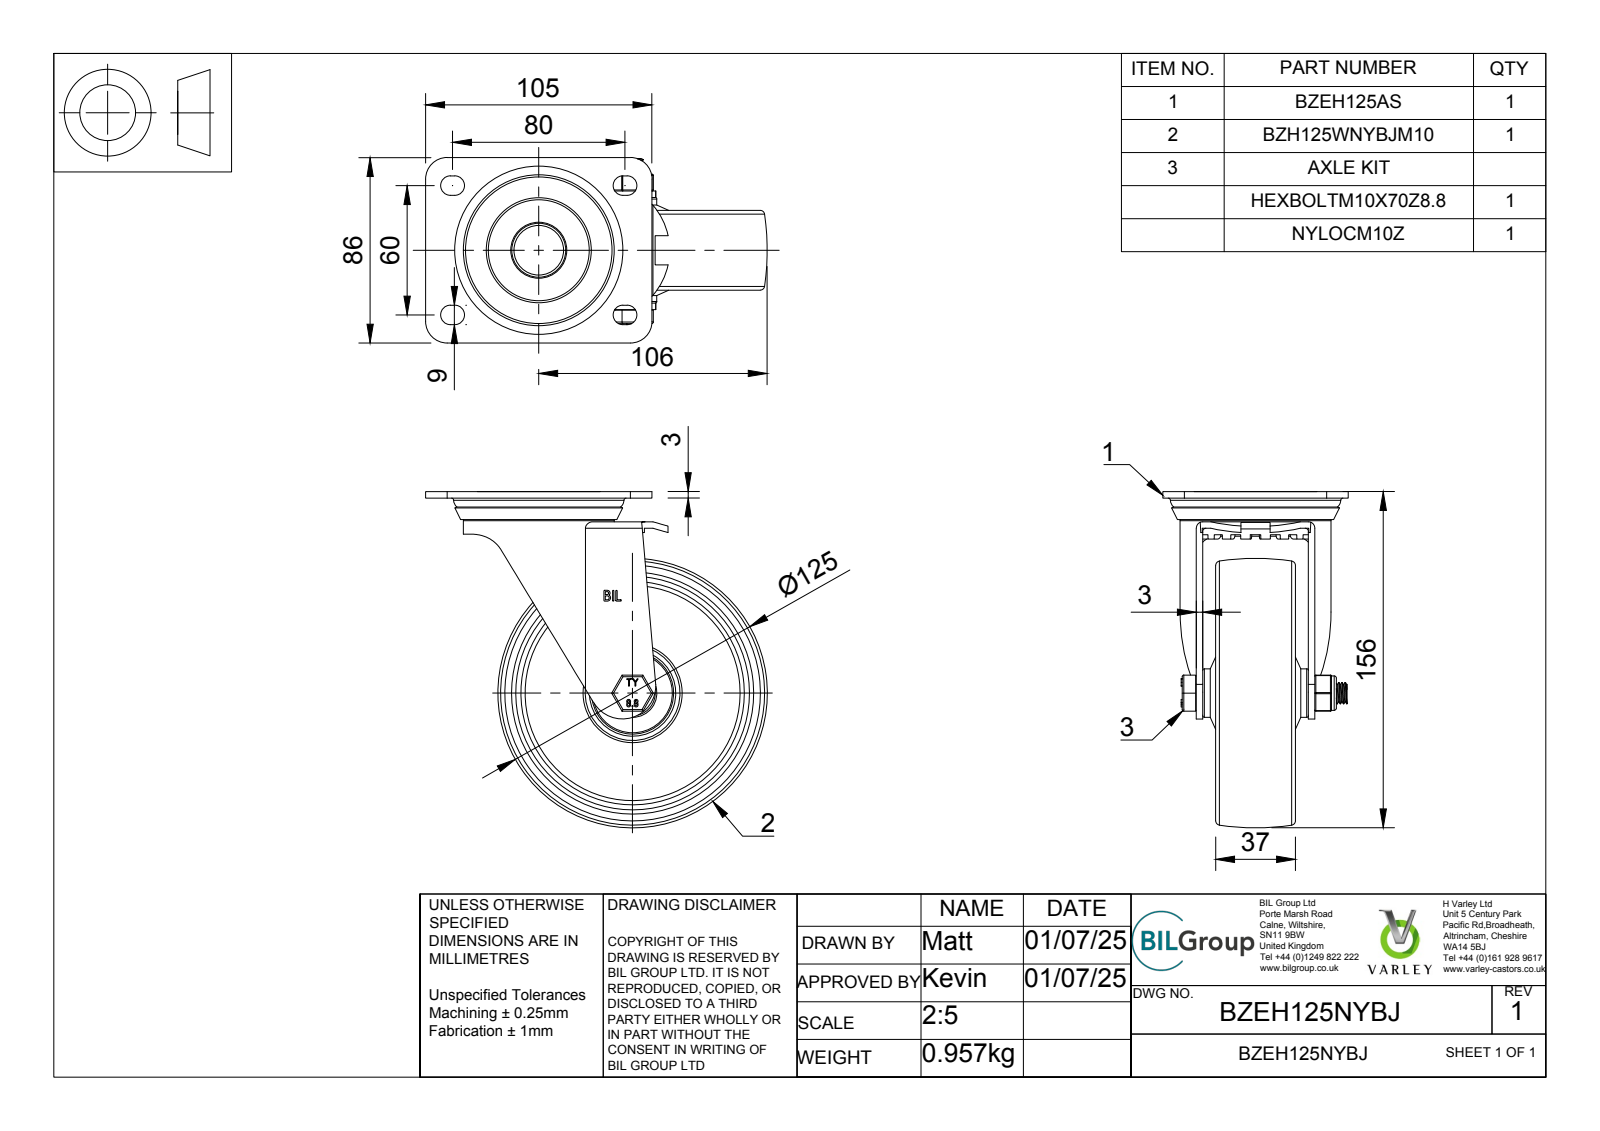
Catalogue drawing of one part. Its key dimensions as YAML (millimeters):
part_name: "BZEH125NYBJ v3; BZH125WNYBJM10 v1; BZMM125WNYBJ; NYLON WHEEL (+7 more)"
step_written_by: "Autodesk Translation Framework v14.10.0.0 (AUTOMOTIVE_DESIGN)"
units: millimeters
bodies: {solids: 42, faces: 881, planar: 389, cylindrical: 173, other: 319}
overall_size: [158.5, 156, 86]
volume: 310368
surface_area: 140189
round_holes:
  - {diameter: 10, count: 1}
  - {diameter: 10.2, count: 1}
  - {diameter: 10.25, count: 1}
  - {diameter: 12, count: 1}
  - {diameter: 15, count: 1}
  - {diameter: 20, count: 1}
  - {diameter: 22.5, count: 1}
  - {diameter: 25, count: 1}
  - {diameter: 30, count: 1}
  - {diameter: 31, count: 1}
  - {diameter: 32, count: 1}
  - {diameter: 34, count: 1}
round_bosses_or_shafts:
  - {diameter: 16, count: 2}
  - {diameter: 70, count: 1}
  - {diameter: 54, count: 1}
  - {diameter: 44, count: 1}
  - {diameter: 38, count: 1}
  - {diameter: 30.5, count: 1}
  - {diameter: 28, count: 1}
  - {diameter: 25, count: 1}
partial_cylinders:
  - {radius: 0.5, count: 18}
  - {radius: 4.5, count: 8}
  - {radius: 0.75, count: 6}
  - {radius: 1.5, count: 4}
  - {radius: 10, count: 4}
  - {radius: 3, count: 2}
  - {radius: 31.61, count: 2}
  - {radius: 12, count: 1}
face_to_face_distances: [3, 7, 24, 21, 28, 9, 52, 31, 15, 6]
